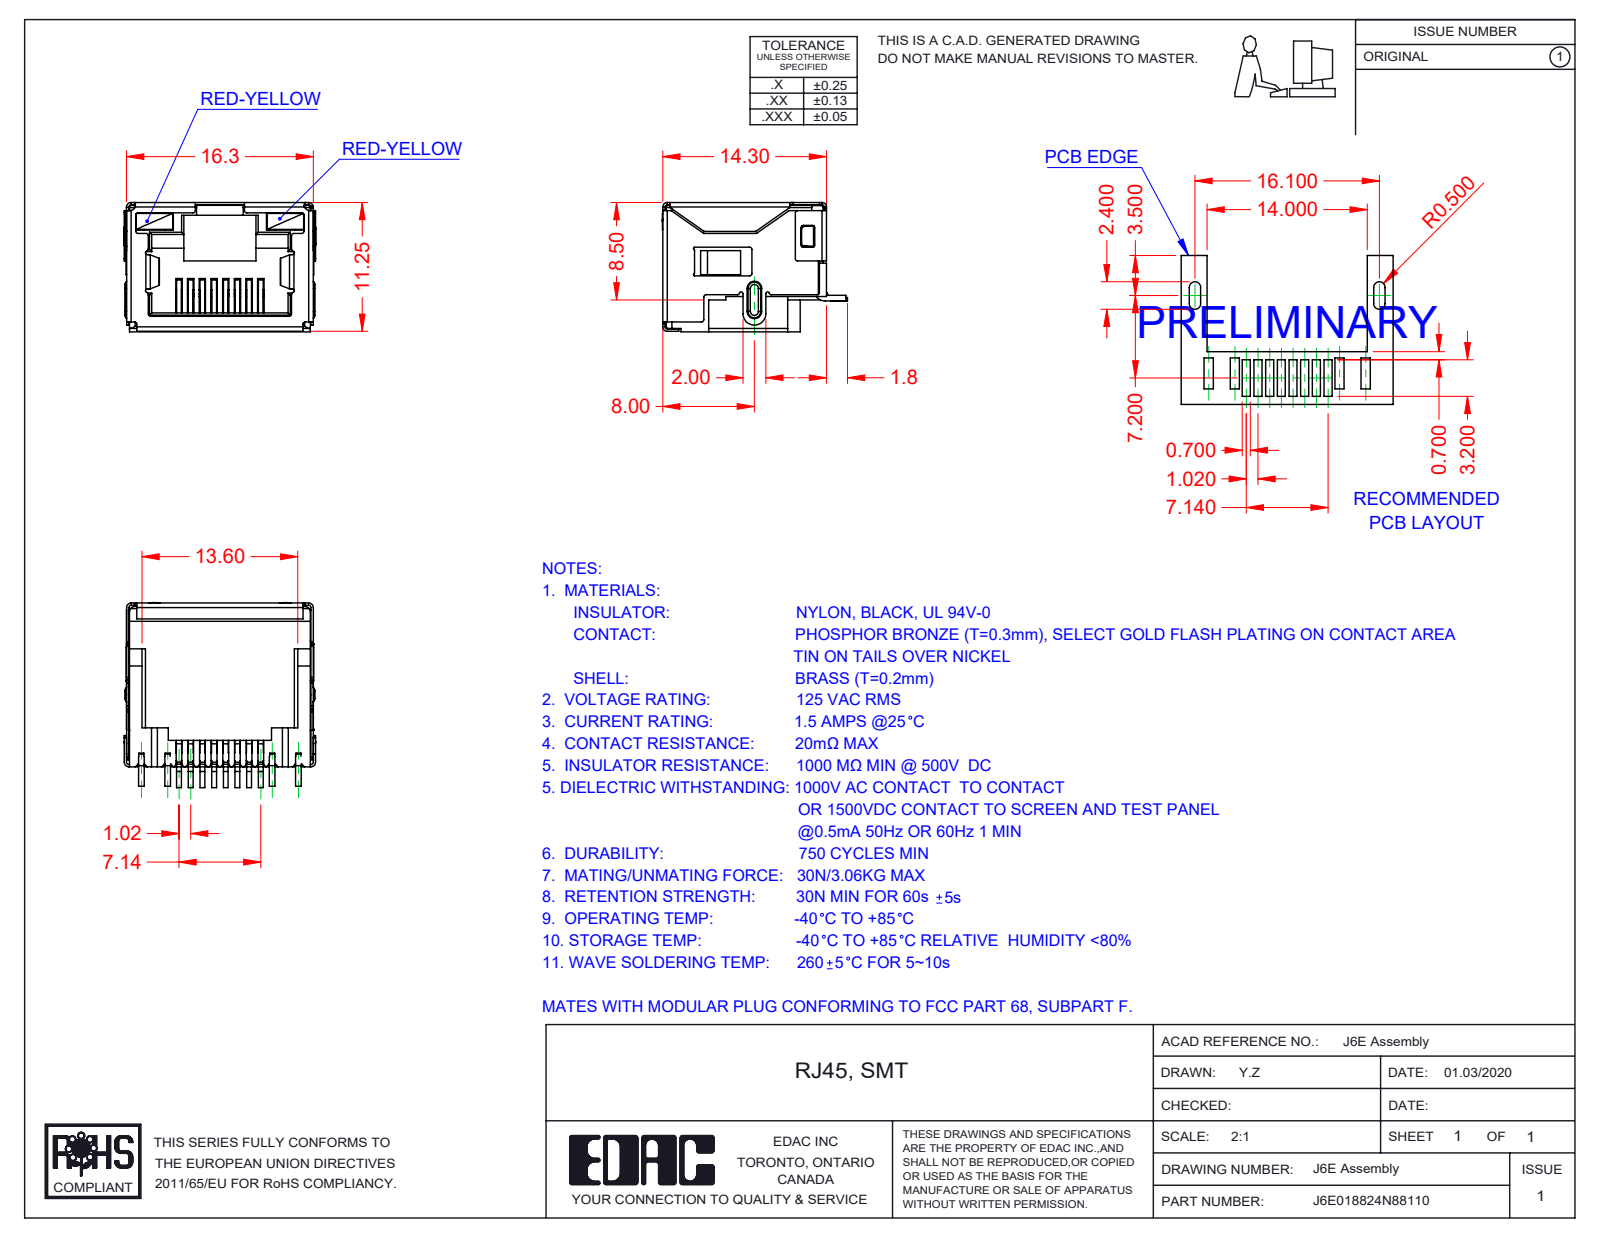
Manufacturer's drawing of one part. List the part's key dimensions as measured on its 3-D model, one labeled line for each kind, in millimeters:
Part name (STEP PRODUCT): J6E018824N88110; 6E Shield_LED; 6E LED RH_8-Red-Yellow; 6E Insulator_LED (+2 more)
STEP written by: SolidWorks 2016 (CONFIG_CONTROL_DESIGN)
Units: millimetres
Bodies: 12 solids, 1500 faces (1099 planar, 351 cylindrical, 50 other)
Overall size (bounding box): 16.75 × 16.15 × 11.3
Volume: 1 109 mm³ · Surface area: 4 045 mm²
Partial cylindrical surfaces — rounded edges, fillets, slot ends (radius × count): R0.2 ×82, R0.25 ×17, R0.4 ×13, R0.5 ×13, R0.1 ×10, R0.15 ×7, R0.3 ×4, R1 ×3
Main face-to-face distances: 11.05, 16.05, 16.1, 15.85, 11.1, 11.3, 2.4, 0.7, 9.85, 0.49
